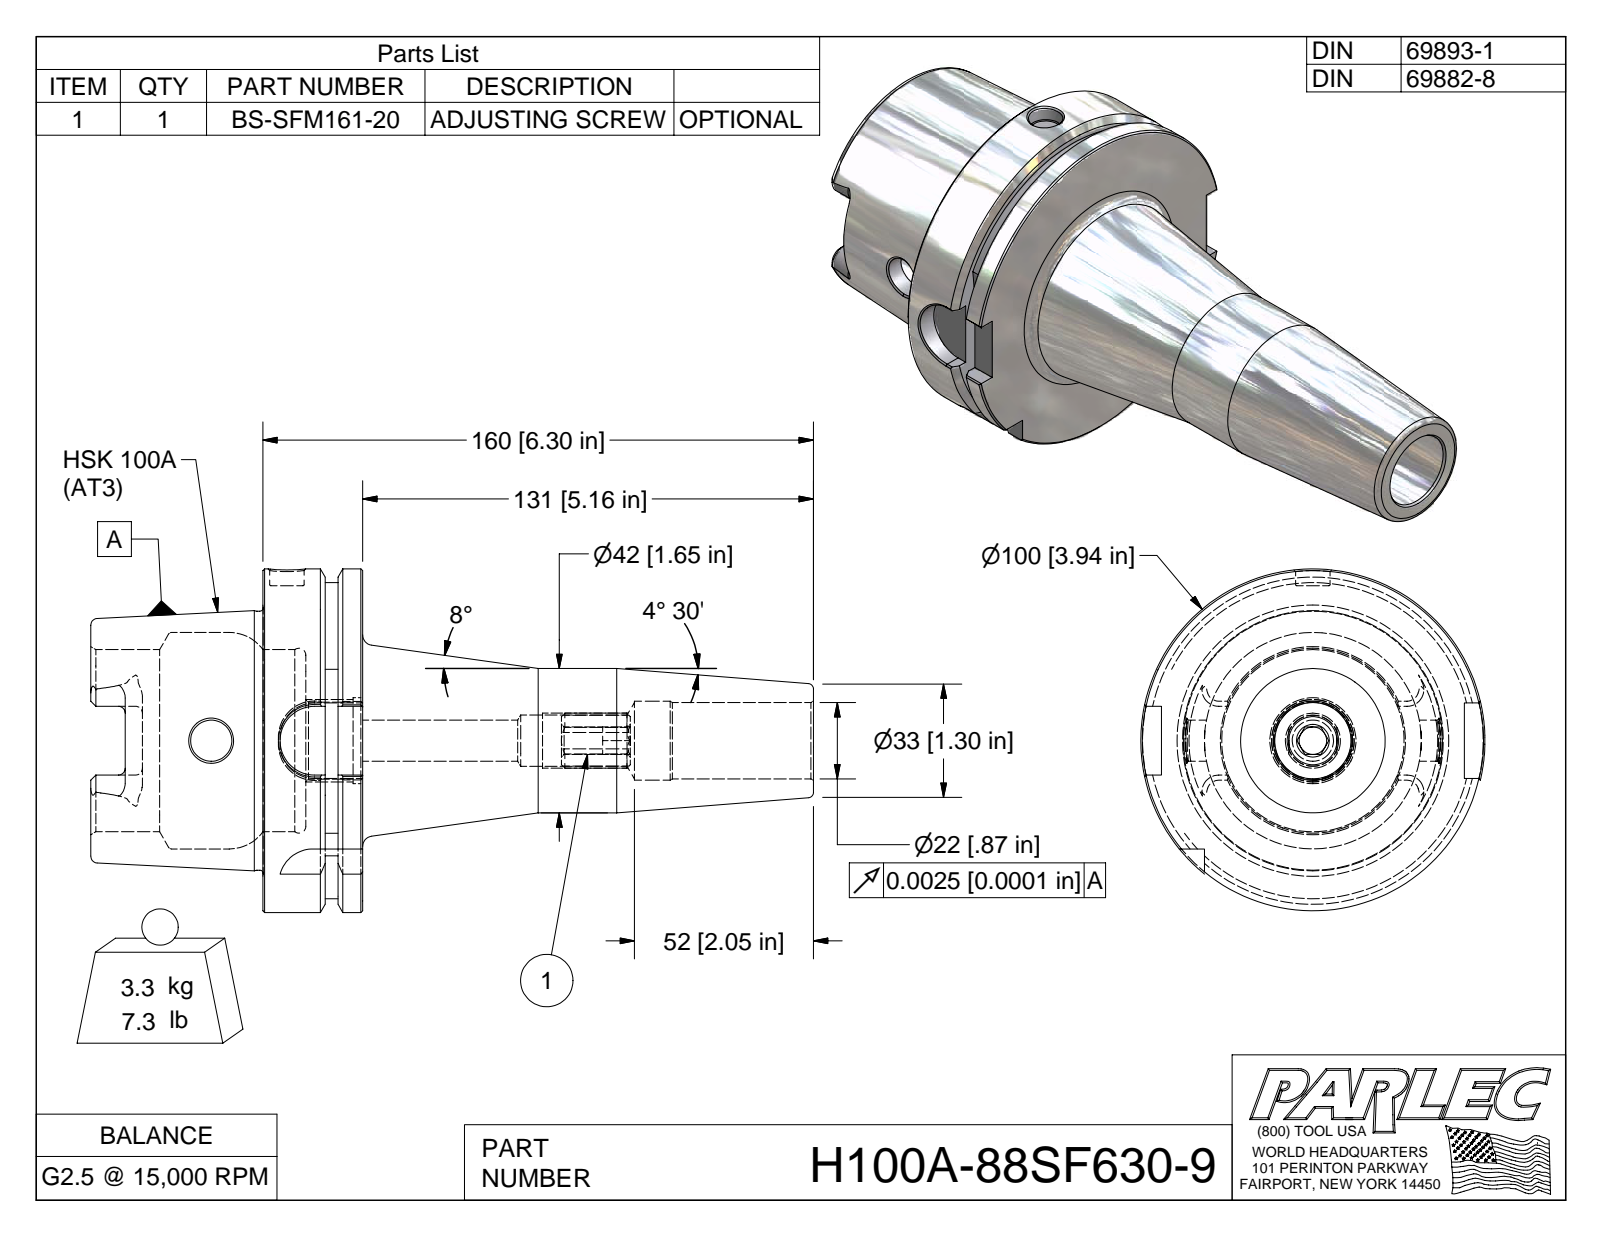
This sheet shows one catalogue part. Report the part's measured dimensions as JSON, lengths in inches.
{"part_name": "H100A-88SF630-9; H100A-88SF630-9-1; BS-SFM161-20", "step_written_by": "Autodesk Inventor 2009 (AUTOMOTIVE_DESIGN)", "units": "inches", "bodies": {"solids": 2, "faces": 151, "planar": 50, "cylindrical": 30, "other": 71}, "overall_size": [8.269, 3.937, 3.937], "volume_in3": 25.49, "surface_area_in2": 115.5, "round_holes": [[0.394, 1], [0.472, 1], [0.874, 1], [0.881, 1], [0.904, 1], [0.985, 1], [2.087, 1], [2.48, 1]], "round_bosses_or_shafts": [[3.937, 1], [2.967, 1], [1.654, 1]], "partial_cylinders_radius": [[0.394, 4], [0.079, 3], [0.192, 2], [0.315, 1], [1.811, 1]], "face_to_face_distances": [1.142, 0.492, 0.65, 1.969, 2.461, 3.11, 2.682, 0.713, 0.221, 0.428]}
